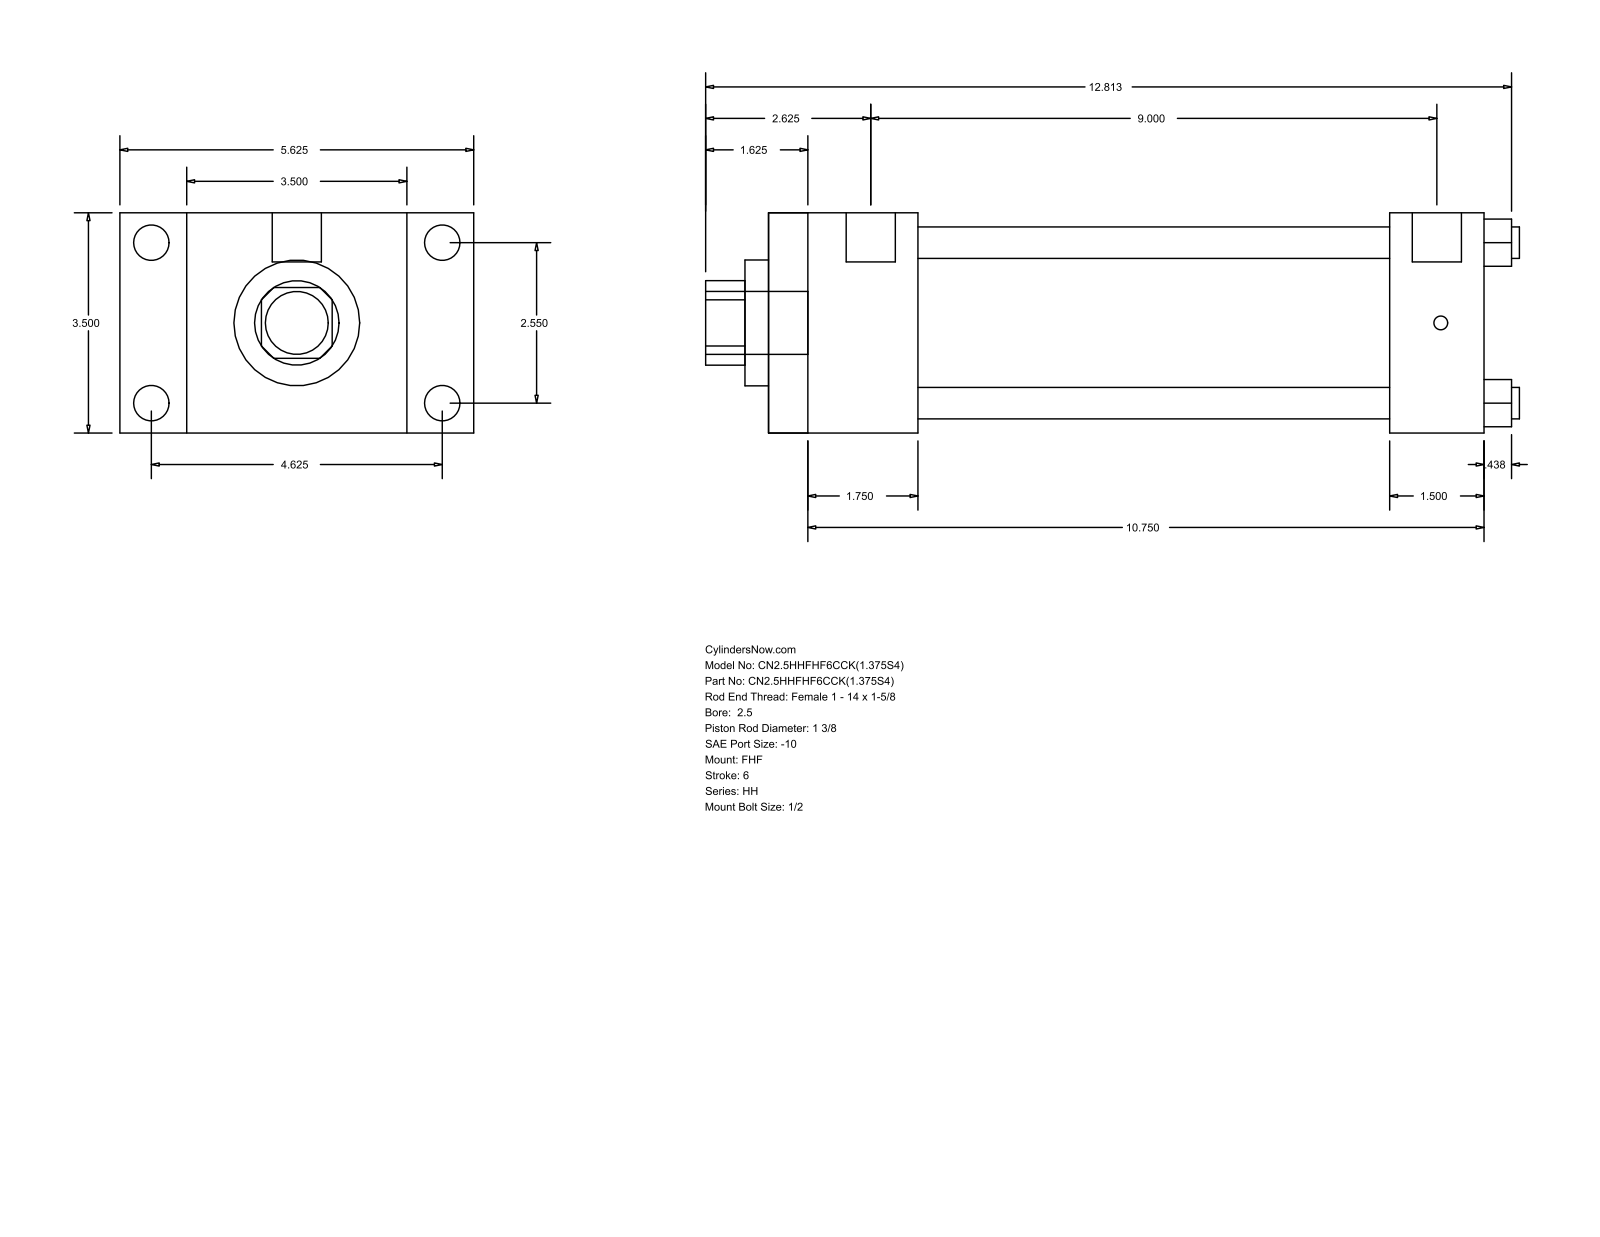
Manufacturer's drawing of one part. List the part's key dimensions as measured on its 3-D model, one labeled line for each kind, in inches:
Part name (STEP PRODUCT): HH_FHF__0250_1.375
STEP written by: GSSL Pune (CONFIG_CONTROL_DESIGN)
Units: inches
Bodies: 0 solids, 88 faces (60 planar, 28 cylindrical, 0 other)
Overall size (bounding box): 12.937 × 5.625 × 3.5
Round holes (diameter × count): ⌀0.5 ×4, ⌀1.375 ×1, ⌀2 ×1, ⌀2.875 ×1
Round bosses / shafts (diameter × count): ⌀0.563 ×4, ⌀0.219 ×4, ⌀0.781 ×2, ⌀1 ×1
Partial cylindrical surfaces — rounded edges, fillets, slot ends (radius × count): R0.672 ×1
Main face-to-face distances: 3.5, 2.375, 1.063, 4.563, 11.375, 9, 5.625, 9.875, 7.5, 1.5
Hole centre spacings: 1.803, 2.55, 3.606
